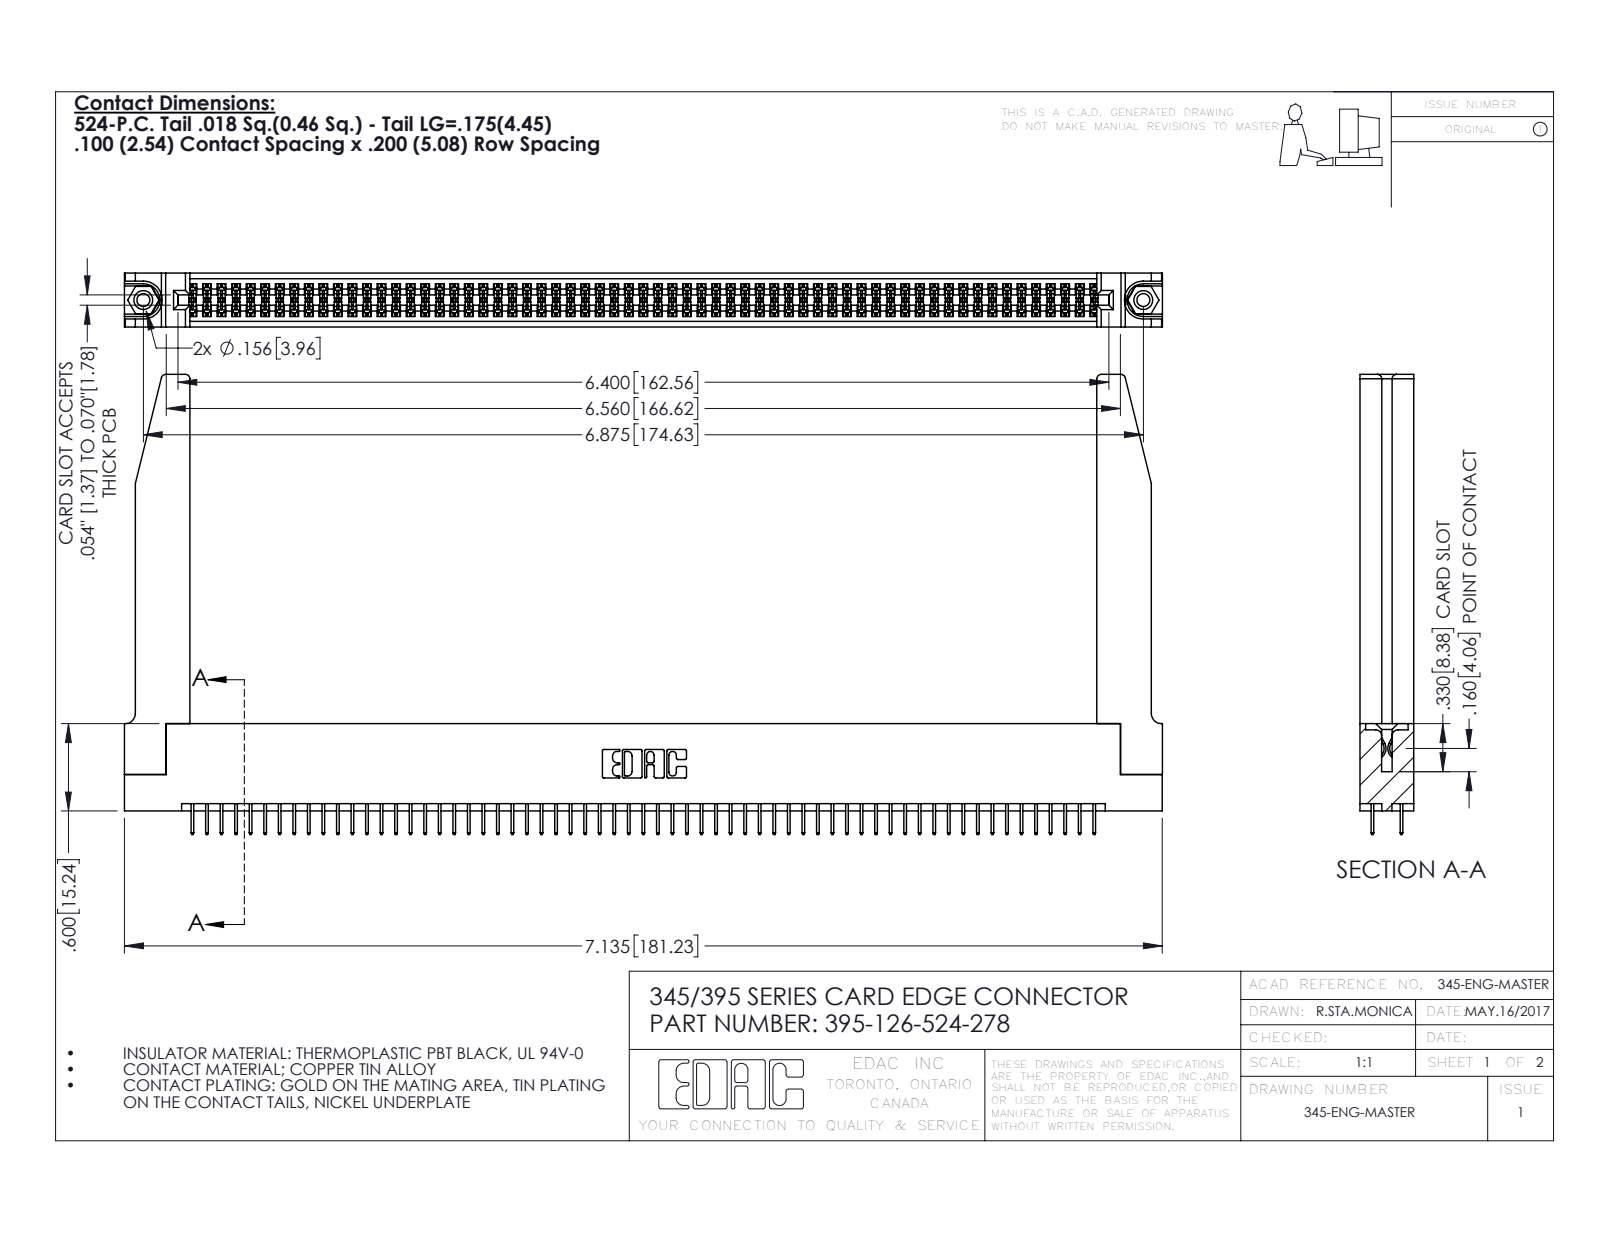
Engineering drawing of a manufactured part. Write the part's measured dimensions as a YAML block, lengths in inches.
part_name: "345-250-001_345-250-001-102; 345 Part_Flush Mounting Lugs - 0.156 Dia-TH; 395-126-524-278; 345-220-078_345-220-078 (+1 more)"
step_written_by: "SolidWorks 2016 (CONFIG_CONTROL_DESIGN)"
units: inches
bodies: {solids: 131, faces: 7164, planar: 5136, cylindrical: 1976, other: 52}
overall_size: [7.136, 3.162, 0.37]
volume: 1.549
surface_area: 50.8
round_holes:
  - {diameter: 0.089, count: 2}
  - {diameter: 0.125, count: 2}
  - {diameter: 0.156, count: 2}
  - {diameter: 0.064, count: 1}
round_bosses_or_shafts:
  - {diameter: 0.155, count: 2}
partial_cylinders:
  - {radius: 0.006, count: 189}
  - {radius: 0.01, count: 22}
  - {radius: 0.03, count: 8}
  - {radius: 0.007, count: 6}
  - {radius: 0.031, count: 6}
  - {radius: 0.026, count: 3}
  - {radius: 0.014, count: 2}
  - {radius: 0.019, count: 2}
face_to_face_distances: [0.072, 0.37, 0.298, 0.2, 0.098, 0.272, 0.025, 0.225, 0.072, 0.175]
hole_center_spacings: [0.27, 6.639, 6.875]
